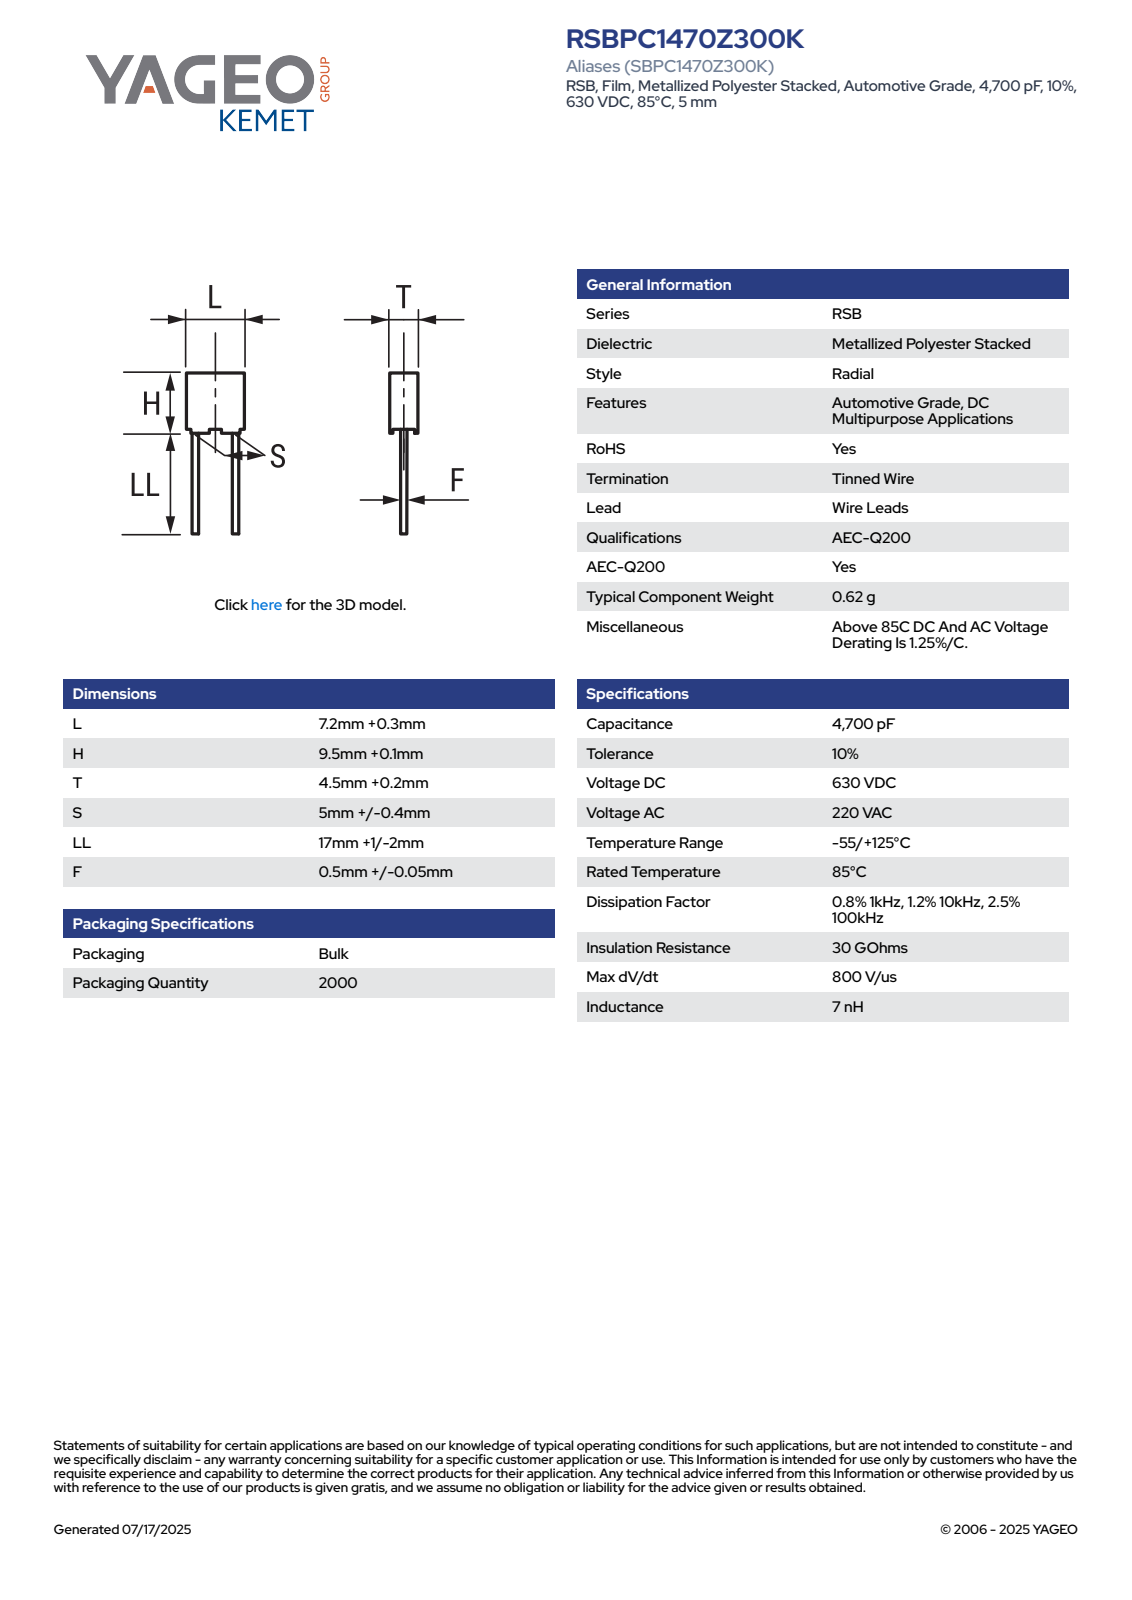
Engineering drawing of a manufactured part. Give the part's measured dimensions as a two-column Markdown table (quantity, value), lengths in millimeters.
| quantity | value |
| --- | --- |
| part name | CFR_RB3_7.2X9.5X4.5_L7.5H9.6T4.7S5LL18F0.65 |
| STEP written by | SolidWorks 2014 (AUTOMOTIVE_DESIGN) |
| units | millimeters |
| bodies | 4 solids, 85 faces (77 planar, 8 cylindrical, 0 other) |
| overall size | 27.6 × 7.5 × 4.71 |
| volume | 327 mm³ |
| surface area | 395 mm² |
| round bosses / shafts (diameter × count) | 0.65 × 2 |
| partial cylindrical surfaces (radius × count) | 0.5 × 4 |
| main face-to-face distances | 4.7, 7.5, 8.85, 4.45, 7.25, 0.75, 9.6, 4.2, 7, 4.71 |
